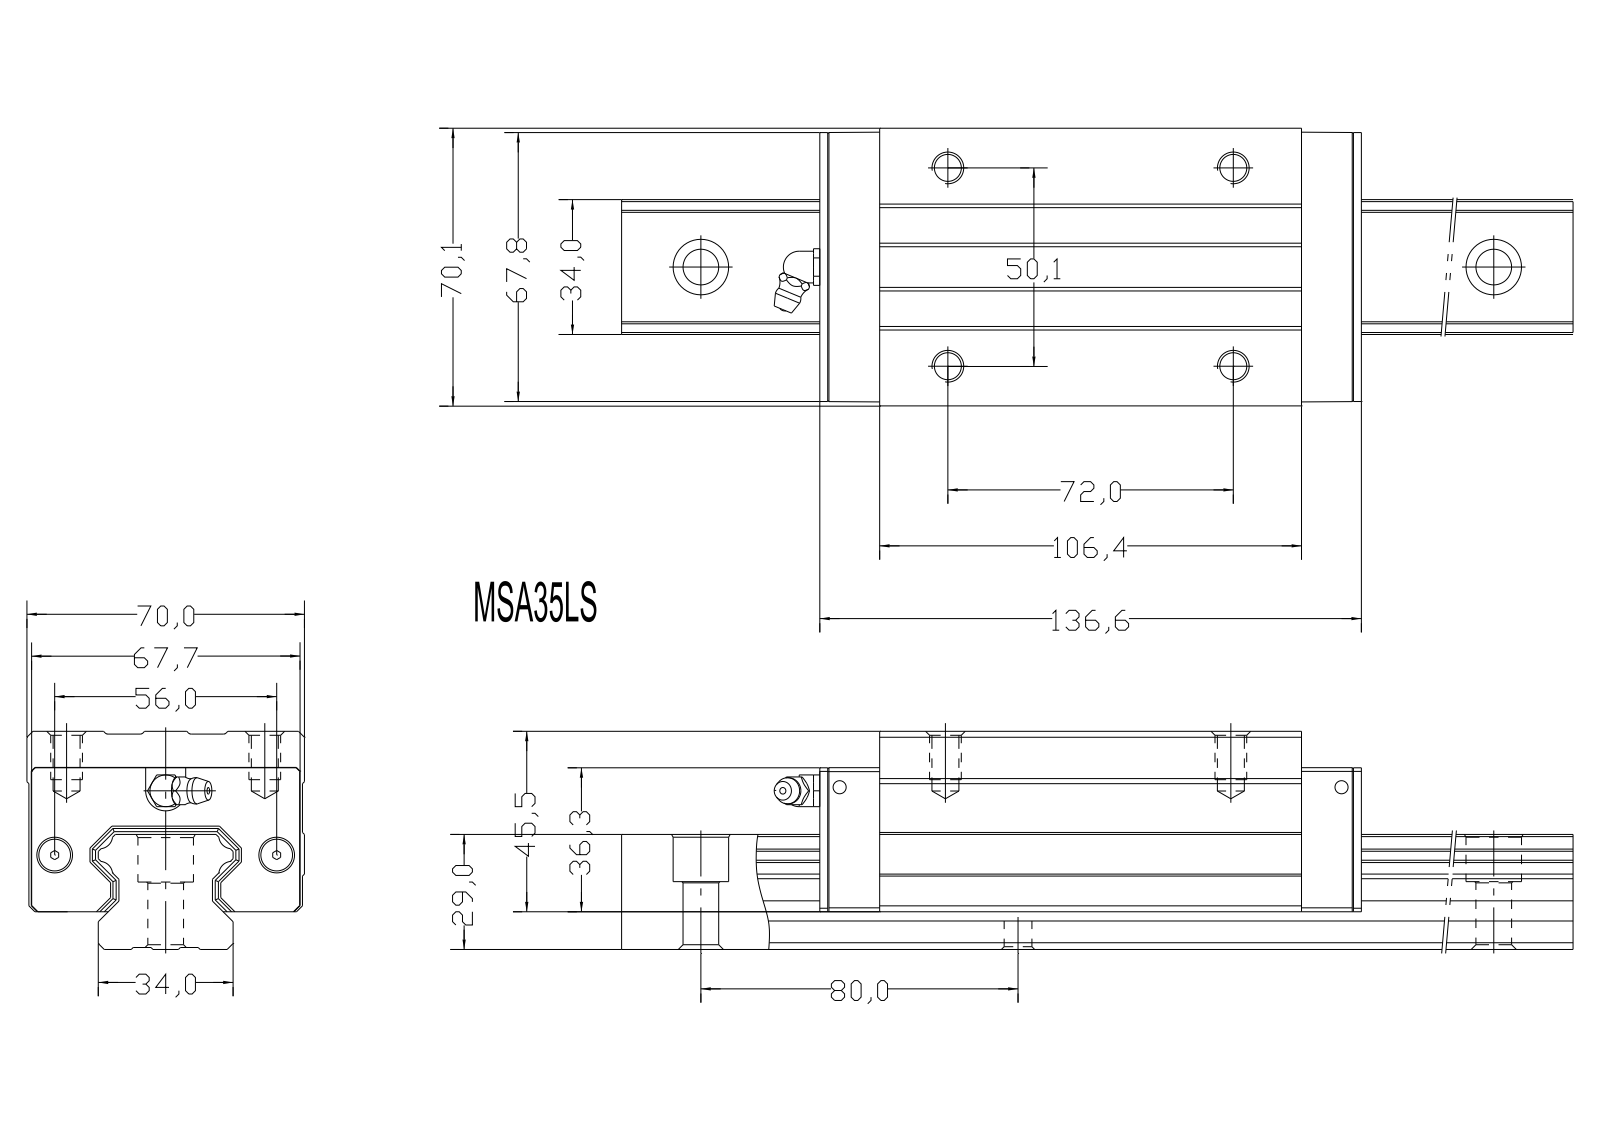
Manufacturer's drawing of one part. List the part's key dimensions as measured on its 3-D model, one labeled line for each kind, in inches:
STEP written by: Kubotek KeyCreator V6.5.2 (0407) (CONFIG_CONTROL_DESIGN)
Units: inches
Bodies: 3 solids, 214 faces (143 planar, 54 cylindrical, 17 other)
Overall size (bounding box): 11.024 × 2.756 × 2.165
Volume: 33.8 in³ · Surface area: 133.9 in²
Round holes (diameter × count): ⌀0.354 ×6, ⌀0.315 ×4, ⌀0.551 ×4, ⌀0.177 ×2
Round bosses / shafts (diameter × count): ⌀0.315 ×1
Partial cylindrical surfaces — rounded edges, fillets, slot ends (radius × count): R0.138 ×4, R0.199 ×1
Main face-to-face distances: 1.791, 0.028, 1.142, 0.768, 0.374, 2.165, 1.024, 0.898, 1.819, 2.138
Hole centre spacings: 0.997, 3.15, 3.45, 6.22, 3.15, 1.969, 2.835, 3.451
